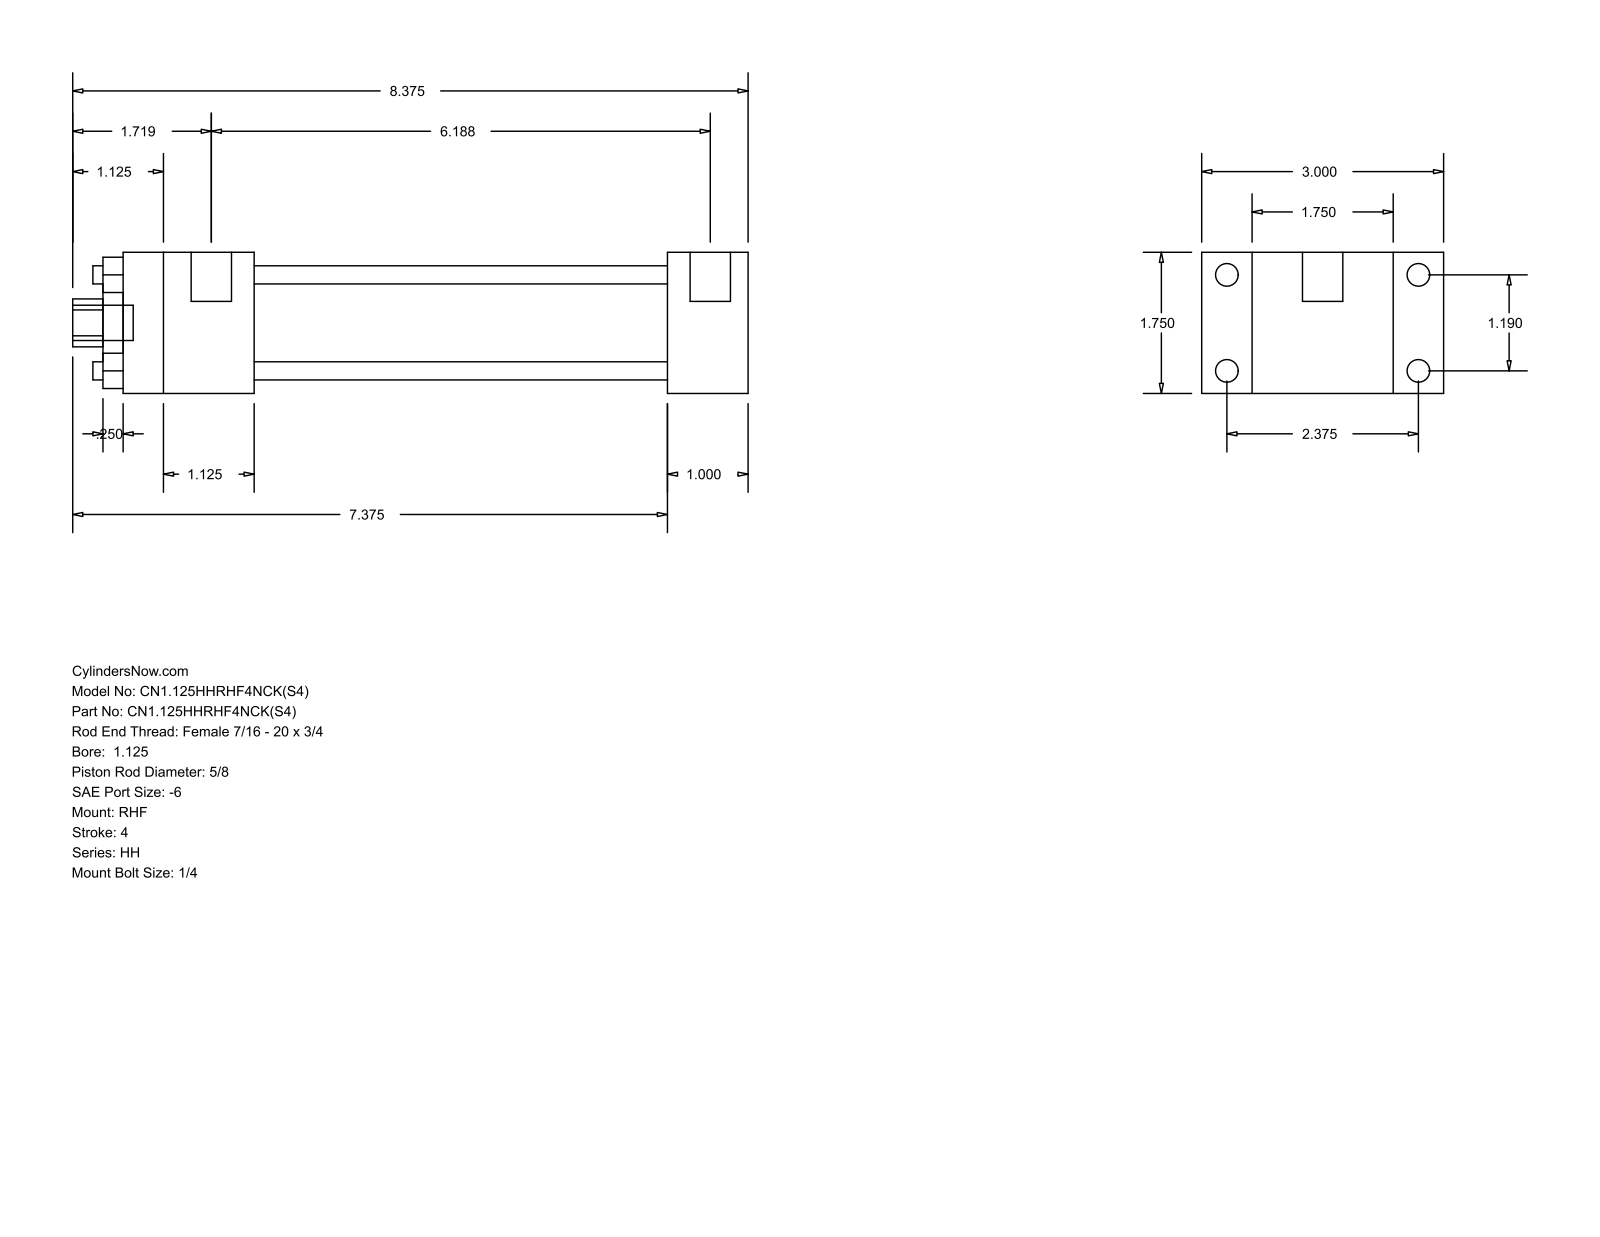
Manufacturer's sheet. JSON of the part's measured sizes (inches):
{"part_name": "HH_RHF__0112_0.625", "step_written_by": "GSSL Pune (CONFIG_CONTROL_DESIGN)", "units": "inches", "bodies": {"solids": 0, "faces": 88, "planar": 60, "cylindrical": 28, "other": 0}, "overall_size": [8.375, 3, 1.75], "round_holes": [[0.225, 4], [0.625, 1], [1.125, 1], [1.375, 1]], "round_bosses_or_shafts": [[0.281, 4], [0.219, 4], [0.5, 2], [0.437, 1]], "partial_cylinders_radius": [[0.297, 1]], "face_to_face_distances": [1.75, 0.625, 2.375, 1, 3, 5.125, 6.125, 1.625, 6.75, 7.75], "hole_center_spacings": [0.841, 1.19, 1.683]}
